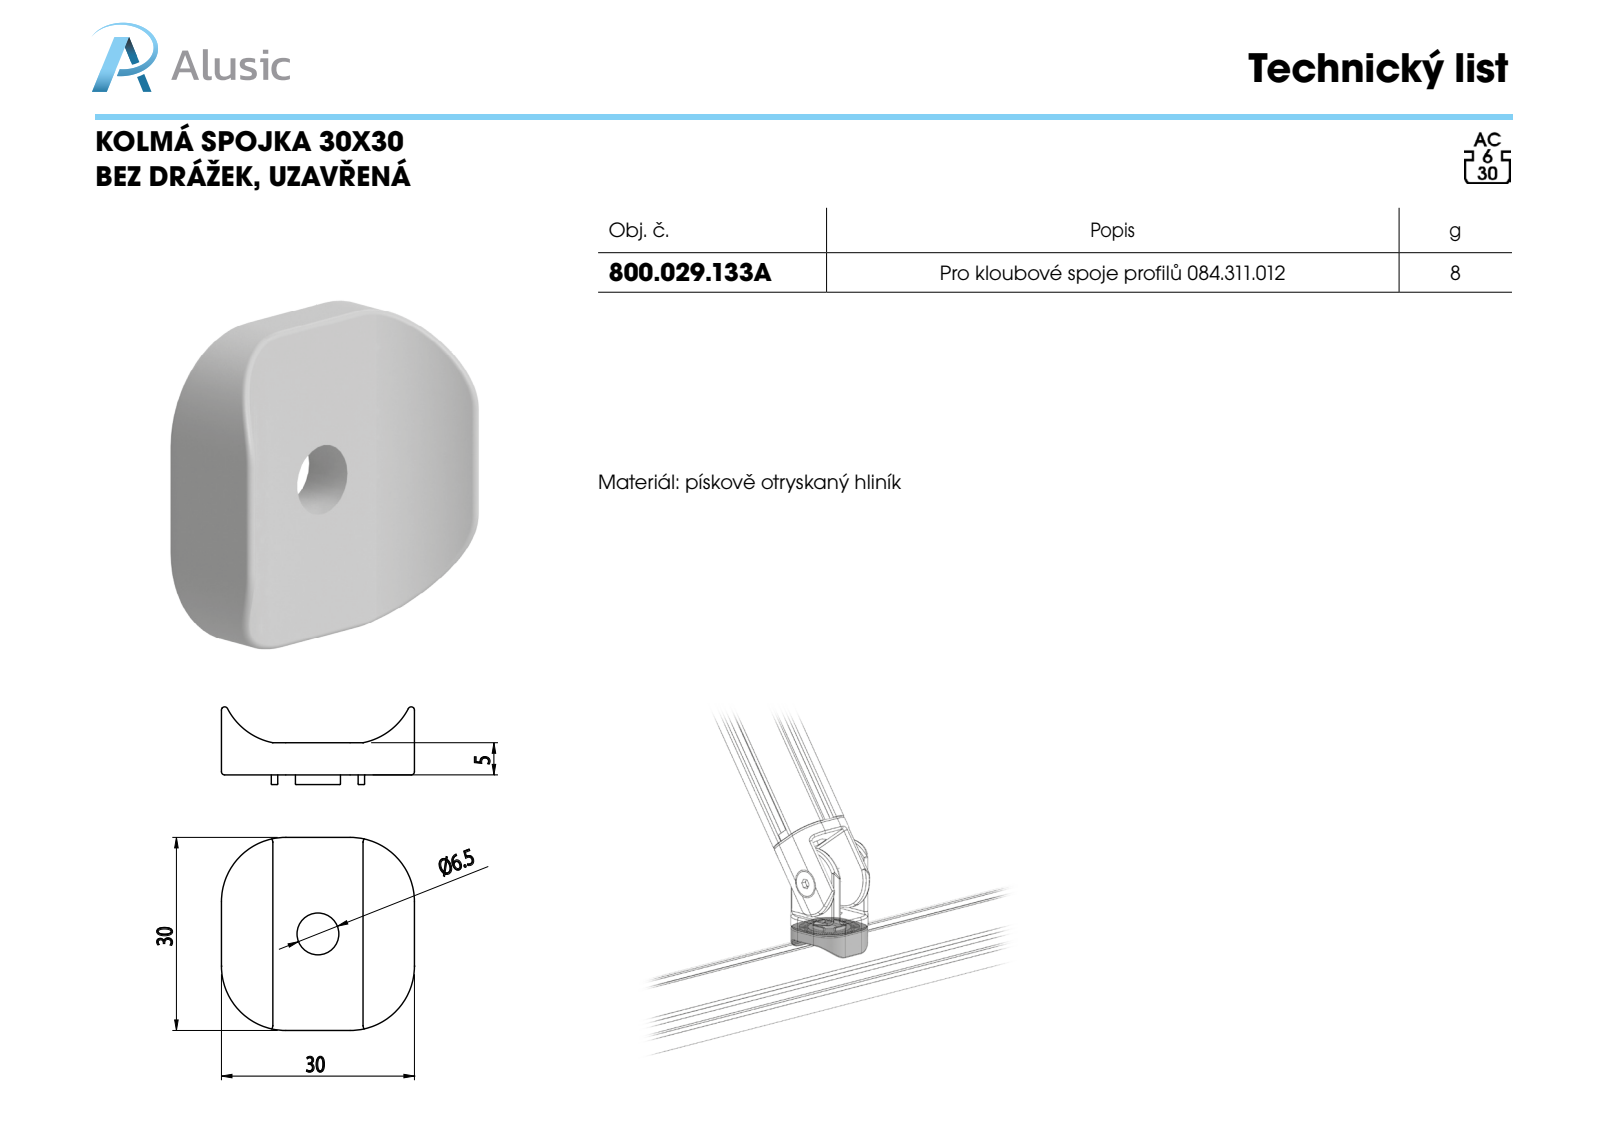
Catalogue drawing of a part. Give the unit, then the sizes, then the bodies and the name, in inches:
Units: inches
Overall size (bounding box): 1.181 × 1.181 × 0.476
Round holes (diameter × count): ⌀0.256 ×1, ⌀1.063 ×1
Round bosses / shafts (diameter × count): ⌀0.748 ×1
Partial cylindrical surfaces — rounded edges, fillets, slot ends (radius × count): R0.004 ×28, R0.02 ×8, R0.394 ×4, R0.402 ×2
Main face-to-face distances: 0.197, 1.181, 0.344, 0.837, 0.876, 0.305, 0.039, 0.531, 0.059, 0.256
Volume: 0.278 in³ · Surface area: 4.29 in²
Bodies: 1 solid, 251 faces (171 planar, 52 cylindrical, 28 other)
Part name (STEP PRODUCT): 800.029.133A
STEP written by: SolidWorks 2012 (CONFIG_CONTROL_DESIGN)
